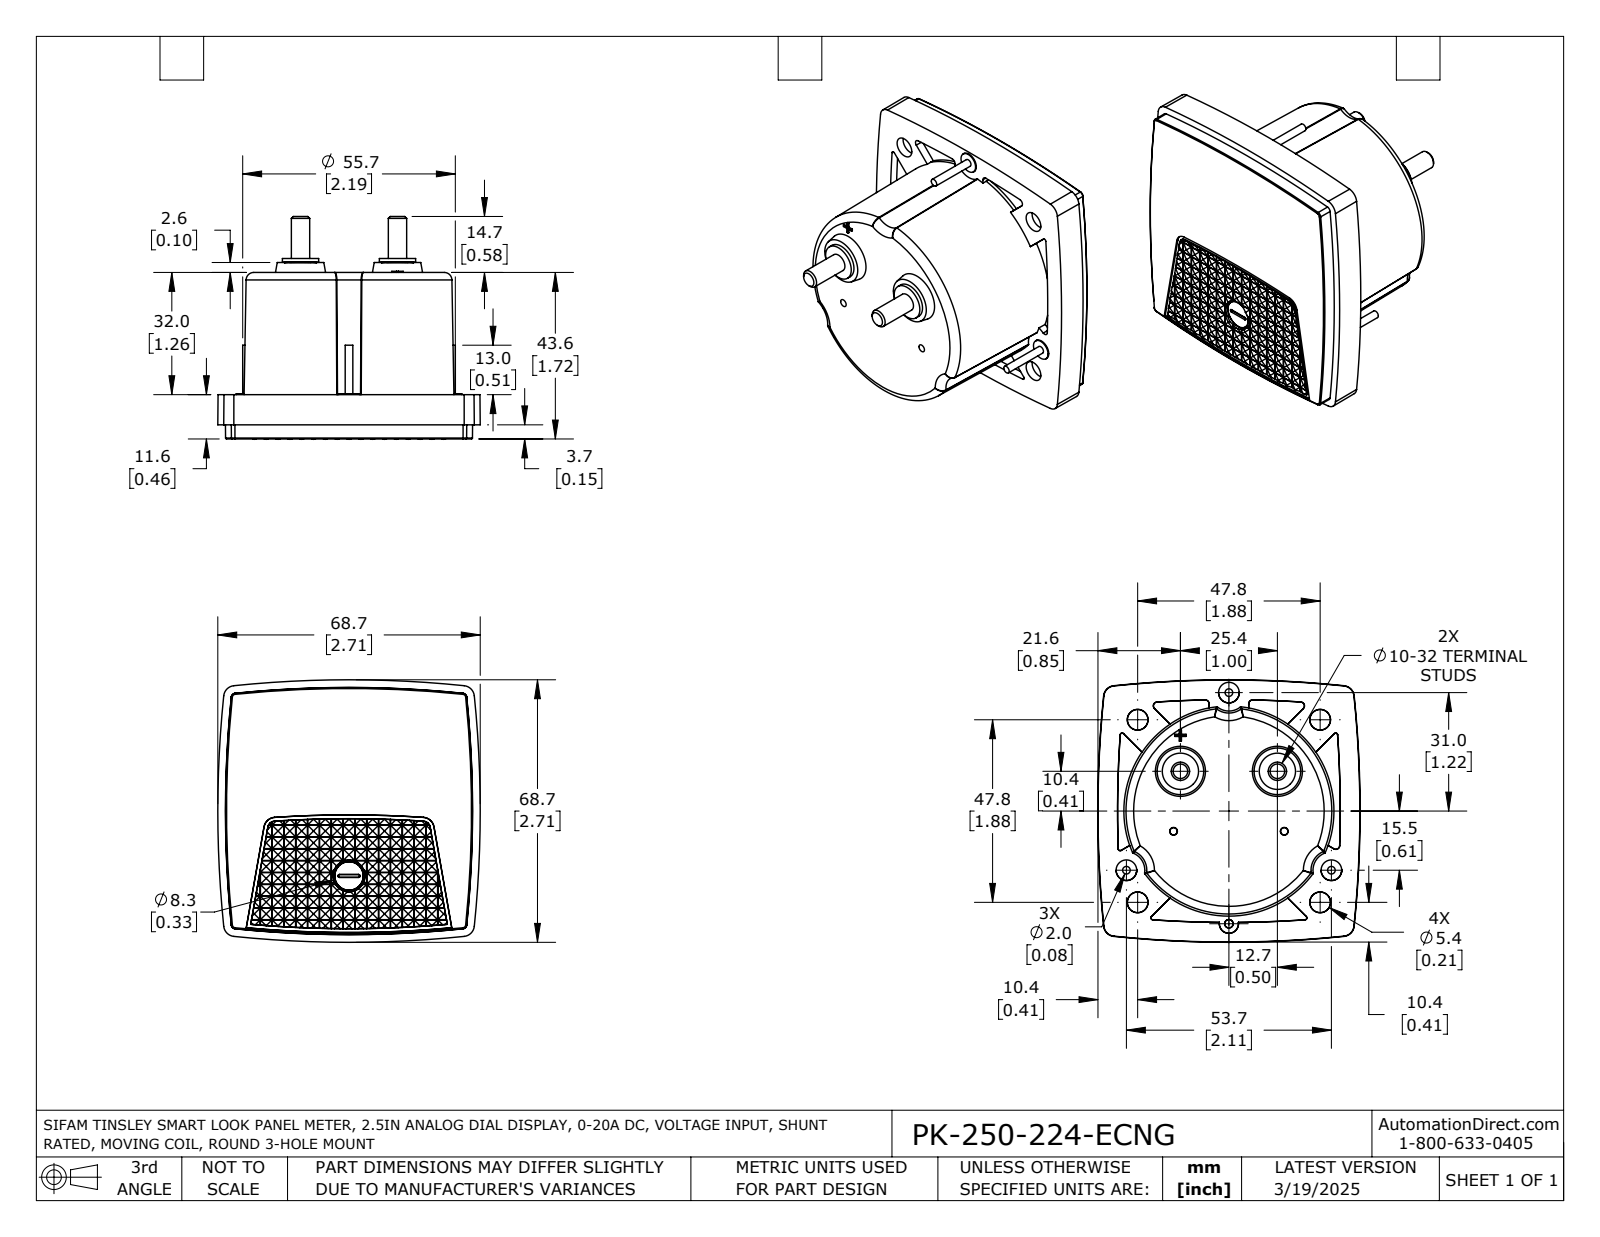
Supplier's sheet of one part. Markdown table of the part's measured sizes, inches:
| quantity | value |
| --- | --- |
| part name | PK-250-224-ECNG |
| STEP written by | SolidWorks 2021 (AUTOMOTIVE_DESIGN) |
| units | inches |
| bodies | 1 solid, 1550 faces (1165 planar, 265 cylindrical, 120 other) |
| overall size | 2.706 × 2.706 × 2.297 |
| volume | 7.594 in³ |
| surface area | 30.41 in² |
| round bosses / shafts (diameter × count) | 0.213 × 3, 0.079 × 3, 0.374 × 2, 0.189 × 2, 0.215 × 1 |
| partial cylindrical surfaces (radius × count) | 0.167 × 2, 1.083 × 1 |
| main face-to-face distances | 1.717, 1.26, 0.457, 0.024, 0.087, 0.096, 0.311, 0.12, 0.072, 1.346 |
